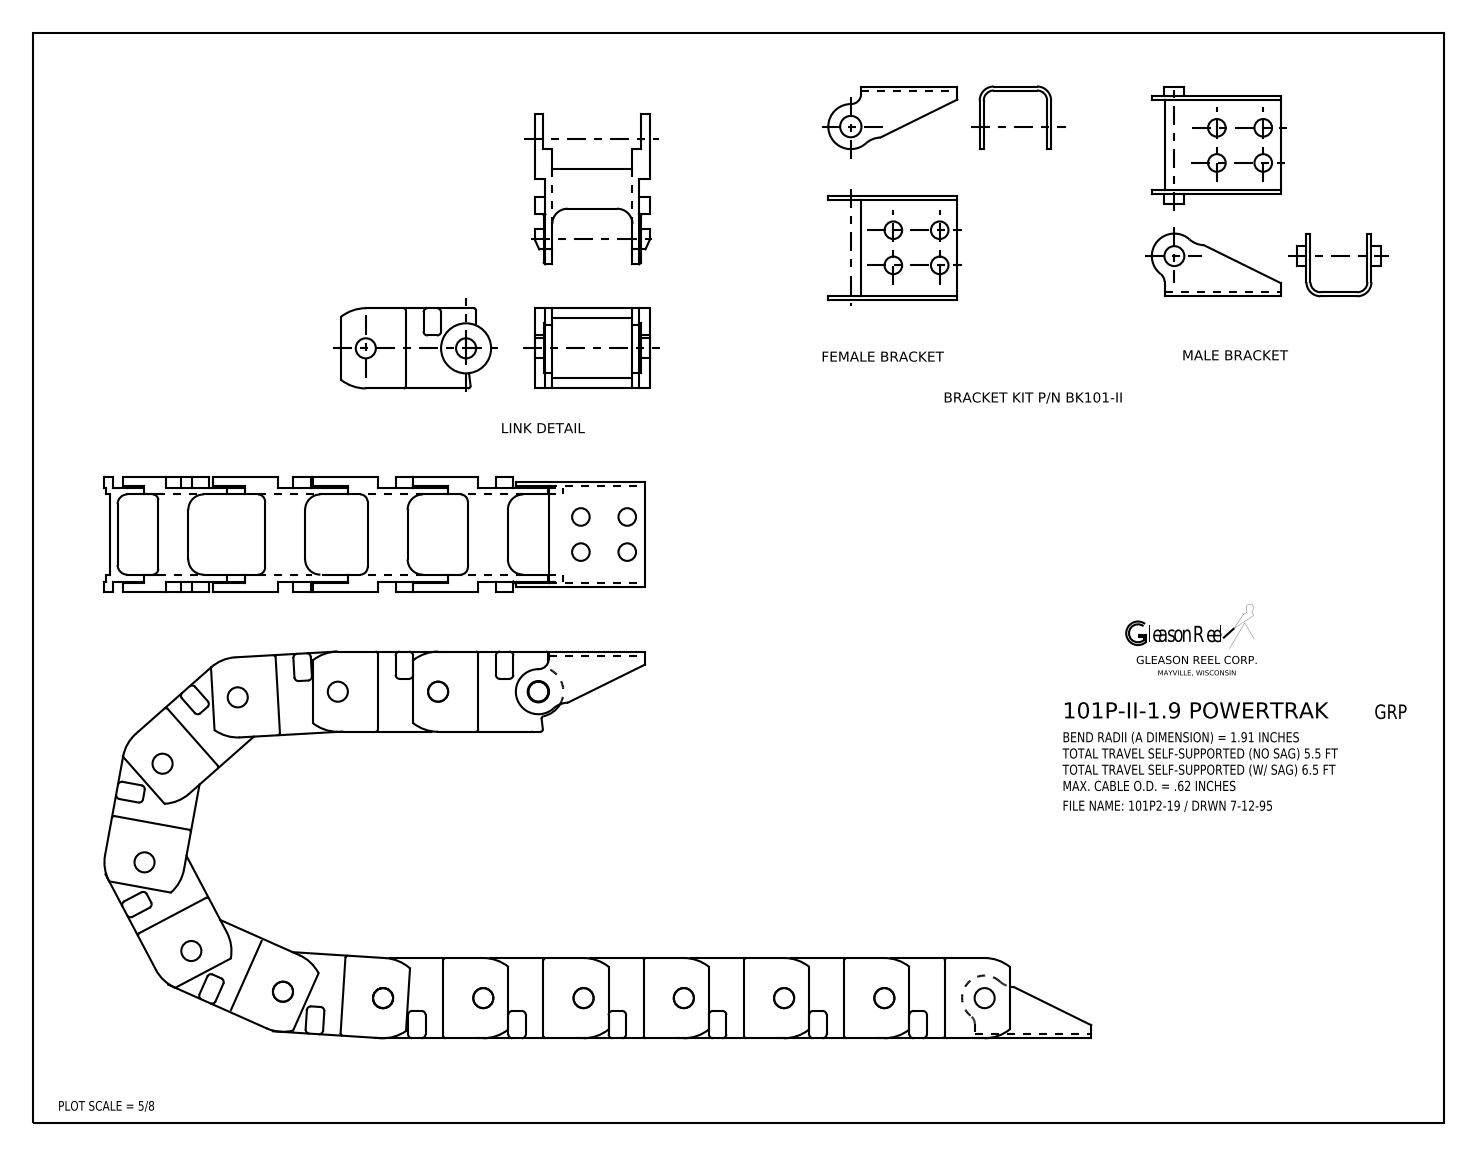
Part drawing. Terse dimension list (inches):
name: 101P2-19
written by: Autodesk Inventor 2013 (AUTOMOTIVE_DESIGN)
unit: in
bodies: 16 solids, 3750 faces (734 planar, 1716 cylindrical, 1300 other)
size: 12.301 × 4.829 × 1.44
volume: 7.712 in³; area: 165.8 in²
holes: 14× ⌀0.25, 8× ⌀0.219, 1× ⌀0.07, 1× ⌀0.266
bosses: 6× ⌀0.25, 1× ⌀0.2
rounds: 548× R0.01, 303× R0.03, 56× R0.035, 56× R0.05, 56× R0.09, 28× R0.015, 28× R0.19, 14× R0.312
face distances: 1.22, 0.22, 1, 0.11, 0.024, 0.11, 1.196, 1.44, 1.306, 1.086
hole spacings: 1.25, 2.5, 0.578, 0.725, 5.563, 3.215, 3.75, 3.861
